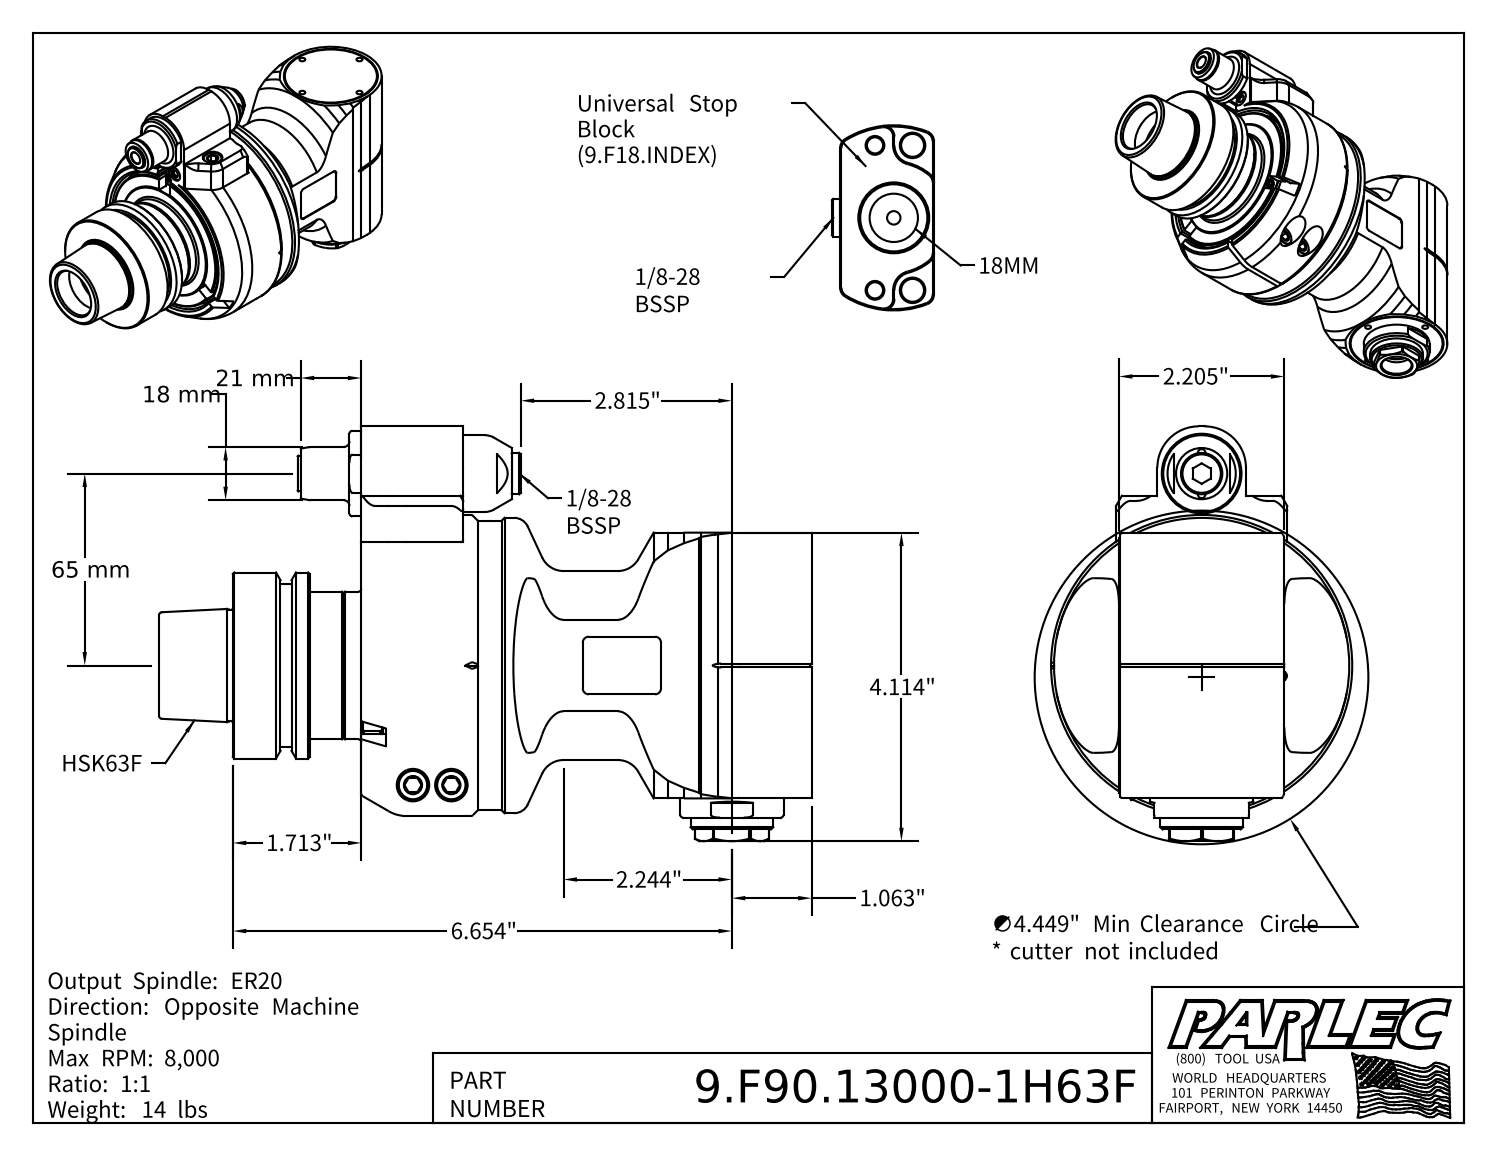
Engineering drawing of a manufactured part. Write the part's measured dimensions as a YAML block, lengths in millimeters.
part_name: "F901300-0000001C_C66"
step_written_by: "Autodesk Inventor 2020 (AUTOMOTIVE_DESIGN)"
units: millimeters
bodies: {solids: 1, faces: 593, planar: 262, cylindrical: 154, other: 177}
overall_size: [221, 140.5, 102]
volume: 956311
surface_area: 110895
round_holes:
  - {diameter: 3.2, count: 4}
  - {diameter: 6.5, count: 3}
  - {diameter: 2.6, count: 2}
  - {diameter: 3.3, count: 2}
  - {diameter: 4.2, count: 2}
  - {diameter: 8, count: 2}
  - {diameter: 10.4, count: 2}
  - {diameter: 11, count: 2}
  - {diameter: 12.5, count: 2}
  - {diameter: 29, count: 2}
  - {diameter: 2.5, count: 1}
  - {diameter: 3, count: 1}
round_bosses_or_shafts:
  - {diameter: 10, count: 4}
  - {diameter: 18, count: 2}
  - {diameter: 12, count: 2}
  - {diameter: 8, count: 2}
  - {diameter: 6, count: 2}
  - {diameter: 2.5, count: 2}
  - {diameter: 102, count: 1}
  - {diameter: 100, count: 1}
partial_cylinders:
  - {radius: 1, count: 14}
  - {radius: 2, count: 12}
  - {radius: 3, count: 6}
  - {radius: 4, count: 4}
  - {radius: 0.4, count: 2}
  - {radius: 0.5, count: 2}
  - {radius: 8, count: 2}
  - {radius: 14, count: 2}
face_to_face_distances: [26, 8.5, 0.5, 56, 52, 7, 43.5, 8, 44, 1.5]
hole_center_spacings: [21.5, 30.41, 7, 12.81, 18.79, 21.54, 25.3, 43]
